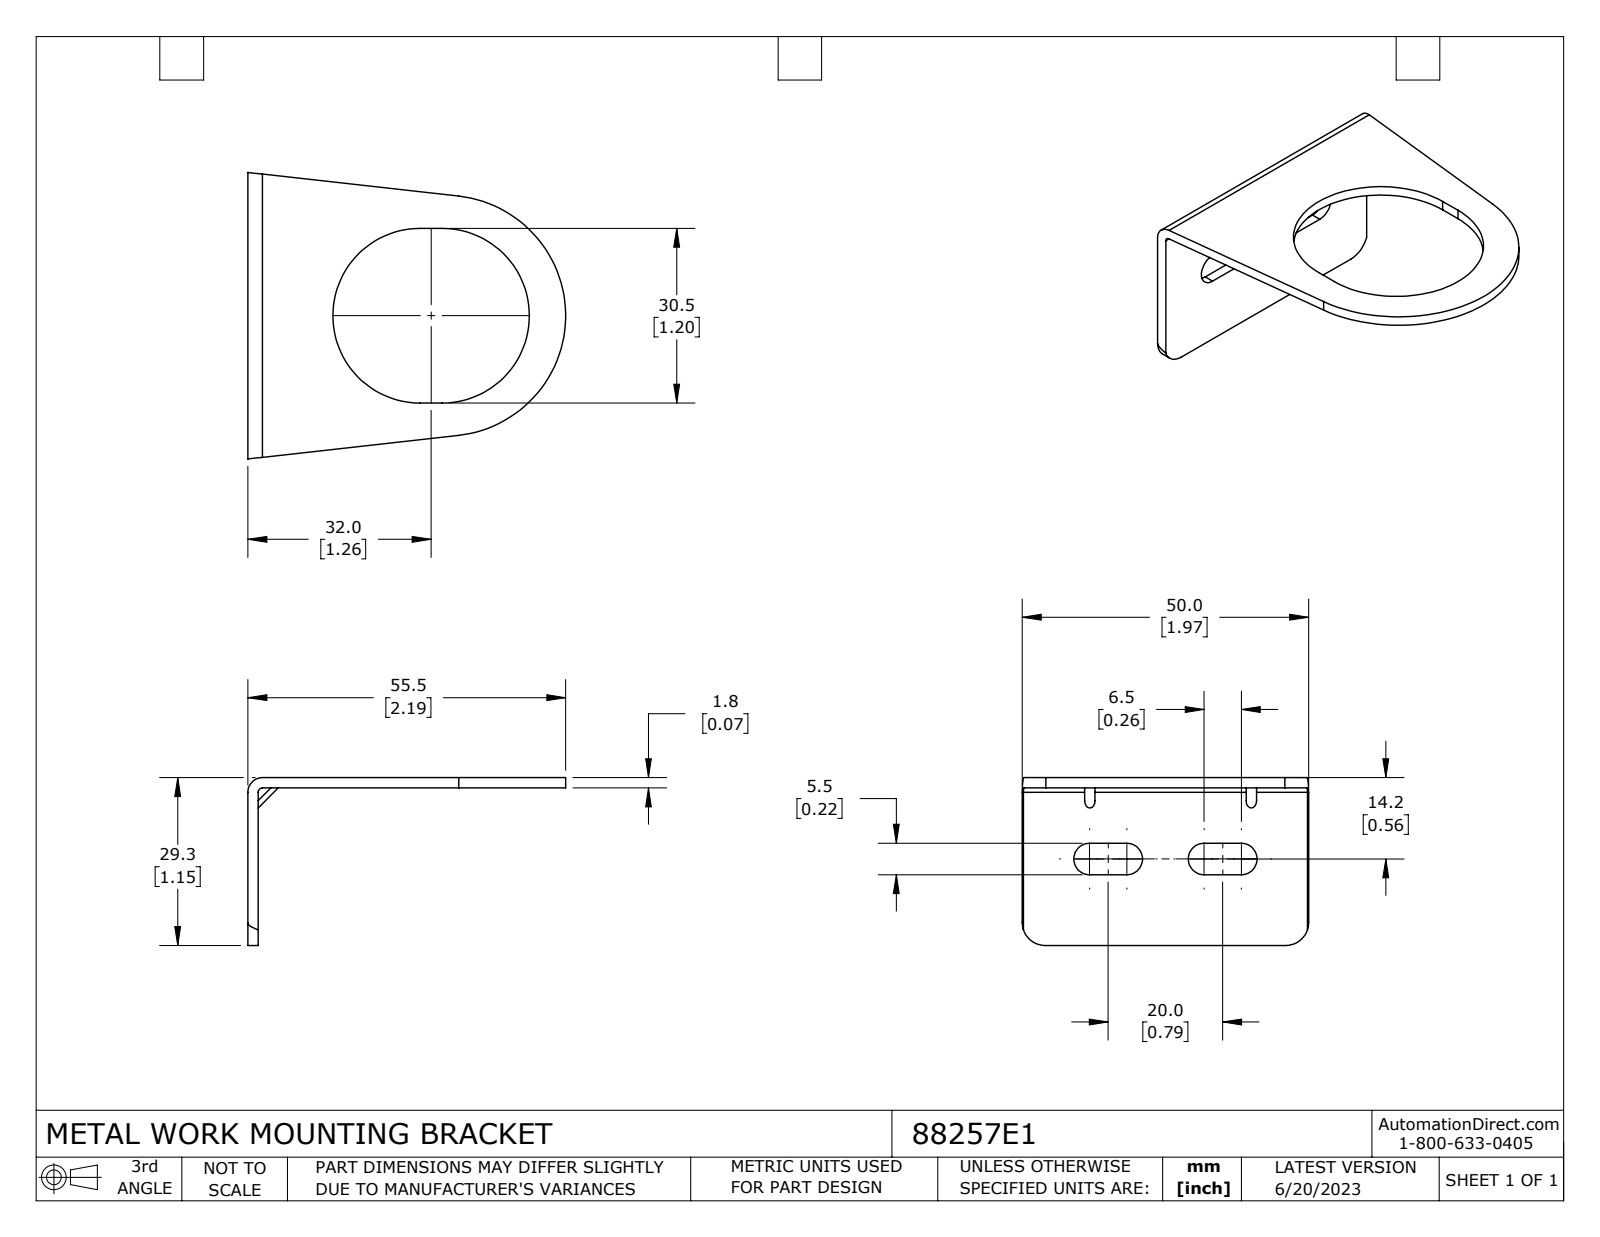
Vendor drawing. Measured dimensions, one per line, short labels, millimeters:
name: 88257E1
written by: SolidWorks 2021 (CONFIG_CONTROL_DESIGN)
unit: mm
bodies: 1 solid, 36 faces (17 planar, 19 cylindrical, 0 other)
size: 55.5 × 50 × 29.3
volume: 4 790 mm³; area: 6 025 mm²
rounds: 4× R2.7, 2× R0.9, 2× R4, 2× R15.2, 1× R0.8, 1× R2.5, 1× R21
face distances: 1.8, 29.3, 27.5, 11.5, 16.9, 9.7, 15.1, 5.5, 17.9, 12.3
